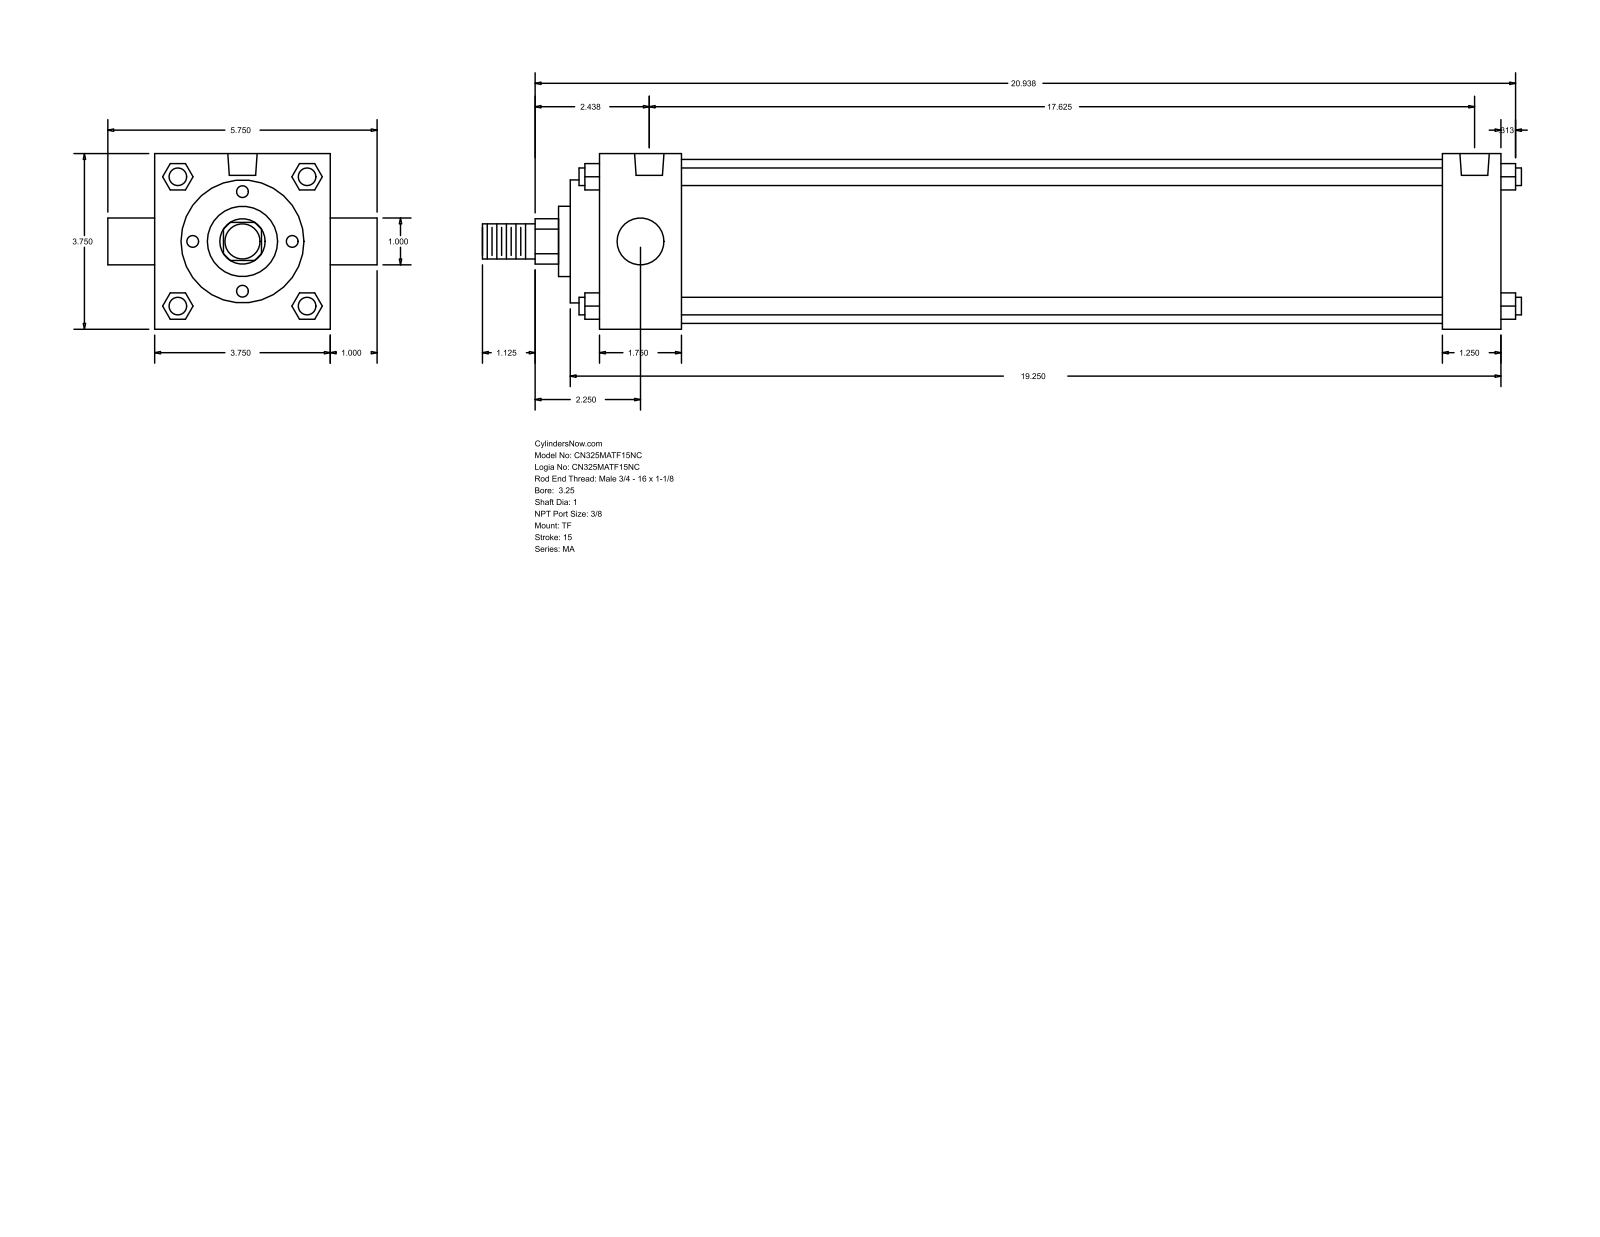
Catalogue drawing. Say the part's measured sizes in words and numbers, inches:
The part is named "MA_TF__0325_1". Its 3-D file was written by "GSSL Pune (CONFIG_CONTROL_DESIGN)". It is 0 solids with 122 faces: 93 planar, 29 cylindrical and 0 other. Overall it measures 22.187 by 5.75 by 3.75 inches. Round holes: 3 of diameter 0.437, 2 of diameter 0.627. Round bosses or shafts: 4 of diameter 0.375, 2 of diameter 1, 1 of diameter 3.5, 1 of diameter 2.625, 1 of diameter 1.5, 1 of diameter 0.75. Partial cylindrical surfaces (rounded edges, fillets, slot ends): 1 of radius 0.484. The main face-to-face distances are 3.75, 19.25, 1.75, 18, 16.25, 17.5, 1.25, 0.625, 2.375, 18.625. The hole center spacings are 0.187, 0.188, 17.25, 17.437, 17.438, 17.625.
